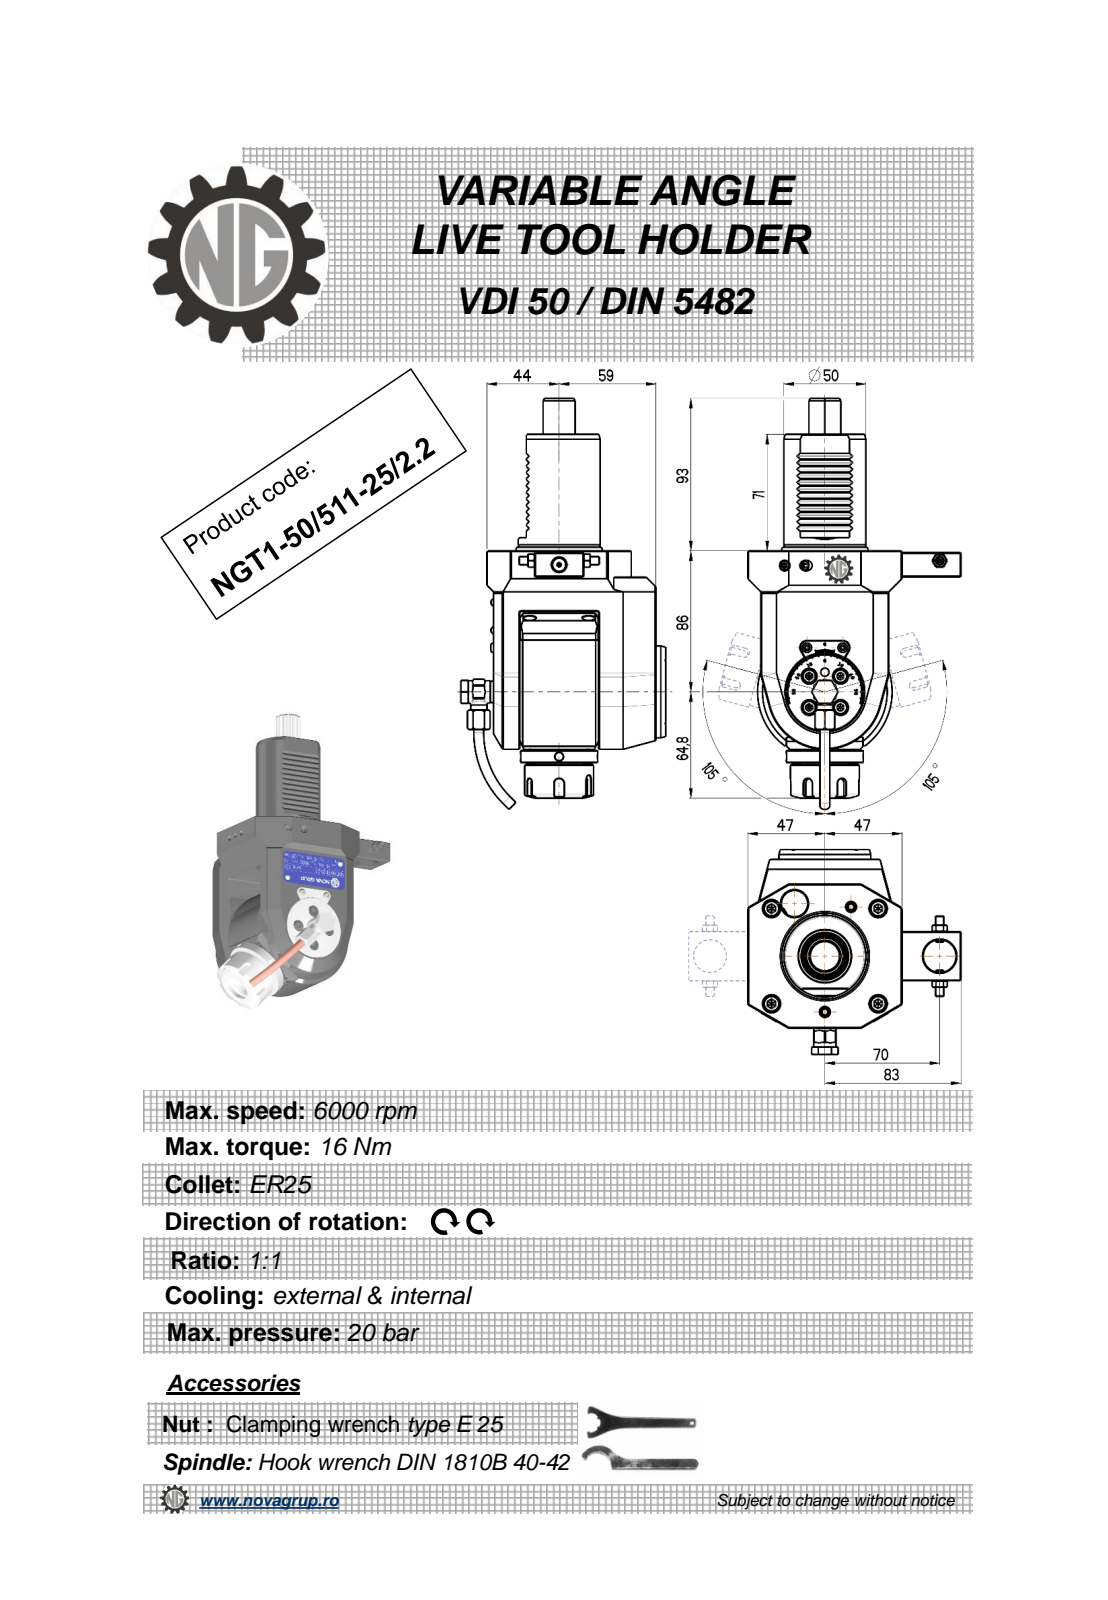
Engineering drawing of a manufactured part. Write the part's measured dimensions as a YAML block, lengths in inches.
part_name: "NGT1_50_511_25_2_2"
step_written_by: "PRO/ENGINEER BY PARAMETRIC TECHNOLOGY CORPORATION, 2010280 (CONFIG_CONTROL_DESIGN)"
units: inches
bodies: {solids: 1, faces: 667, planar: 267, cylindrical: 186, other: 214}
overall_size: [9.869, 5.118, 4.917]
volume: 62.85
surface_area: 141.8
round_holes:
  - {diameter: 0.157, count: 3}
  - {diameter: 0.197, count: 2}
  - {diameter: 0.118, count: 1}
  - {diameter: 0.244, count: 1}
  - {diameter: 0.354, count: 1}
  - {diameter: 0.374, count: 1}
  - {diameter: 0.394, count: 1}
  - {diameter: 0.433, count: 1}
  - {diameter: 0.787, count: 1}
  - {diameter: 0.799, count: 1}
round_bosses_or_shafts:
  - {diameter: 0.236, count: 2}
  - {diameter: 0.224, count: 2}
  - {diameter: 2.205, count: 1}
  - {diameter: 1.969, count: 1}
  - {diameter: 1.85, count: 1}
  - {diameter: 1.654, count: 1}
  - {diameter: 1.378, count: 1}
  - {diameter: 0.535, count: 1}
partial_cylinders:
  - {radius: 0.131, count: 24}
  - {radius: 0.01, count: 12}
  - {radius: 0.012, count: 12}
  - {radius: 0.006, count: 6}
  - {radius: 0.118, count: 5}
  - {radius: 0.02, count: 4}
  - {radius: 0.039, count: 2}
  - {radius: 0.394, count: 2}
face_to_face_distances: [1.457, 3.898, 0.63, 0.315, 0.236, 0.827, 2.52, 4.134, 0.787, 3.071]
hole_center_spacings: [0.016, 1.553, 1.929, 1.945, 2.756, 3.364, 3.373, 4.604]
